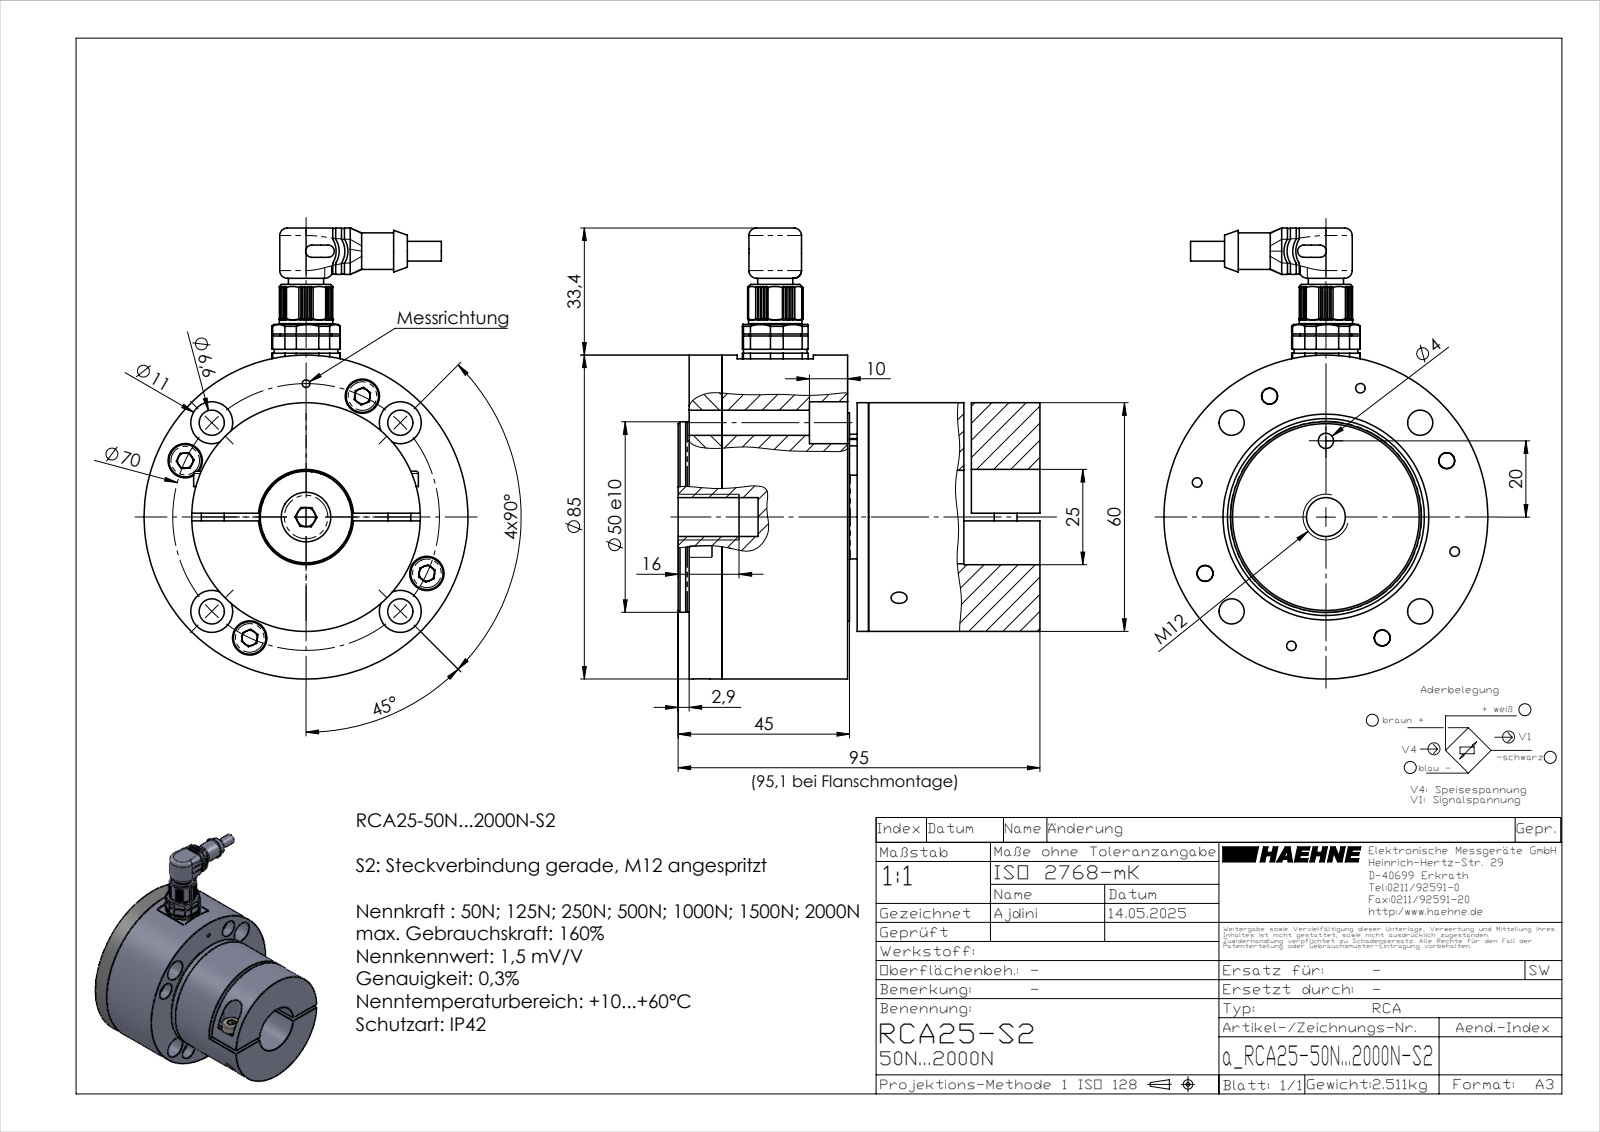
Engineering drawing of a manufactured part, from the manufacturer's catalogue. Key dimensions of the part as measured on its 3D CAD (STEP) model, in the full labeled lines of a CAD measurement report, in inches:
Part name (STEP PRODUCT): inafag_1203-tvh_7zkvytp7yxkimpdvw8sj0b5w4_15; Washer DIN 9021 - 8.4_Washer DIN 9021 - 8.4; DIN 7984 - M8 x 12 --- 8.25N_DIN 7984 - M8 x 12 --- 8.25N; DIN EN ISO 8747-M3x10-St_DIN EN ISO 8747-M3x10-St (+8 more)
STEP written by: SolidWorks 2023 (AUTOMOTIVE_DESIGN)
Units: inches
Bodies: 53 solids, 1226 faces (662 planar, 295 cylindrical, 269 other)
Overall size (bounding box): 4.659 × 3.744 × 3.346
Volume: 22.33 in³ · Surface area: 174.7 in²
Round holes (diameter × count): ⌀0.134 ×9, ⌀0.098 ×8, ⌀0.26 ×6, ⌀0.165 ×5, ⌀0.433 ×5, ⌀0.043 ×4, ⌀0.045 ×4, ⌀0.063 ×4, ⌀0.073 ×4, ⌀0.157 ×4, ⌀0.209 ×4, ⌀0.354 ×4
Round bosses / shafts (diameter × count): ⌀0.118 ×9, ⌀0.224 ×8, ⌀0.335 ×4, ⌀0.197 ×4, ⌀0.071 ×4, ⌀0.061 ×4, ⌀0.059 ×4, ⌀0.039 ×4
Partial cylindrical surfaces — rounded edges, fillets, slot ends (radius × count): R0.008 ×16, R0.012 ×9, R0.016 ×4, R0.021 ×4, R0.039 ×4, R0.05 ×4, R0.236 ×4, R0.063 ×2
Main face-to-face distances: 0.118, 0.079, 0.339, 1.854, 1.772, 0.457, 1.969, 1.181, 1.398, 1.972
Hole centre spacings: 1.378, 1.949, 0.976, 0.992, 1.291, 2.013, 2.223, 0.098
